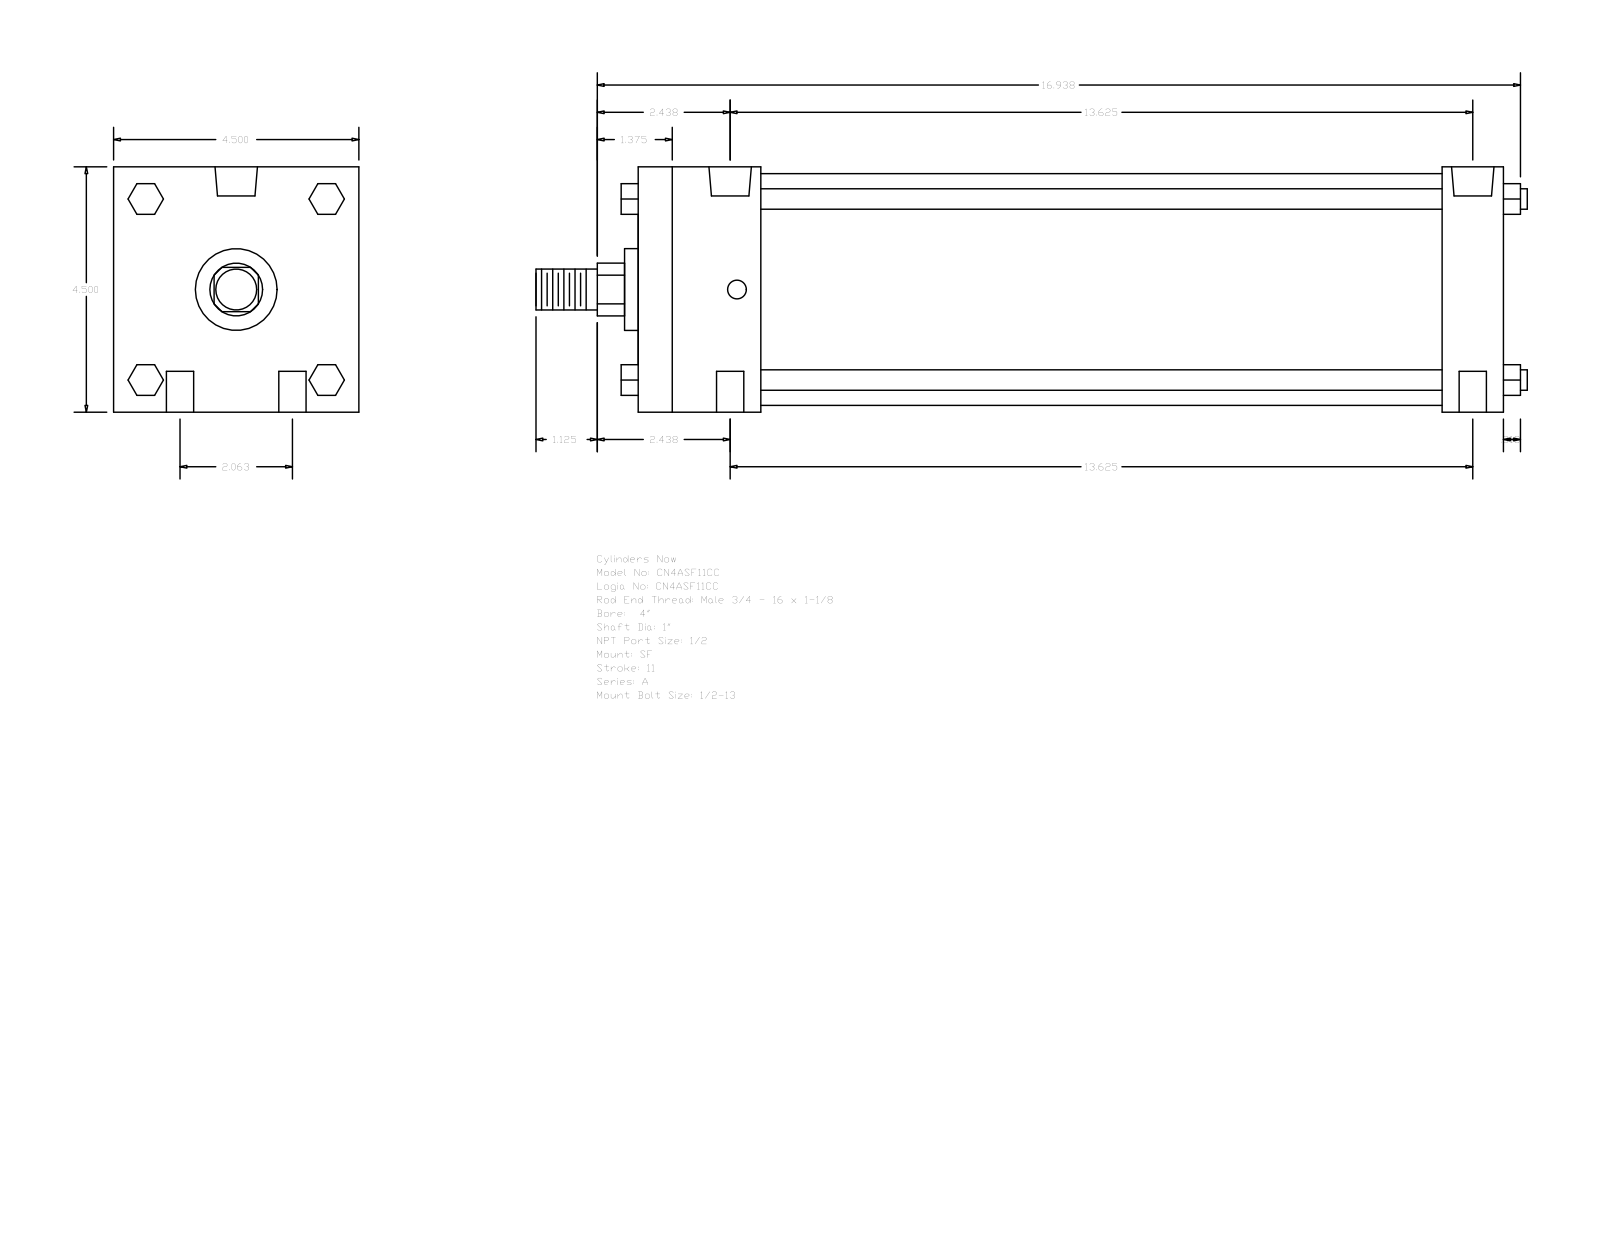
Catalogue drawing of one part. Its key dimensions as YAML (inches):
part_name: "A_SF__0400_1"
step_written_by: "GSSL Pune (CONFIG_CONTROL_DESIGN)"
units: inches
bodies: {solids: 0, faces: 124, planar: 94, cylindrical: 30, other: 0}
overall_size: [18.187, 4.5, 4.5]
round_holes:
  - {diameter: 0.5, count: 4}
  - {diameter: 0.344, count: 2}
  - {diameter: 0.778, count: 2}
round_bosses_or_shafts:
  - {diameter: 0.375, count: 4}
  - {diameter: 4.25, count: 1}
  - {diameter: 1.5, count: 1}
  - {diameter: 1, count: 1}
  - {diameter: 0.75, count: 1}
partial_cylinders:
  - {radius: 0.484, count: 1}
face_to_face_distances: [4.5, 15.875, 1.125, 14.75, 2.25, 12.5, 13.625, 0.563, 1.66, 2.875]
hole_center_spacings: [1.031, 13.664, 13.625, 2.062, 13.78, 13.375]
